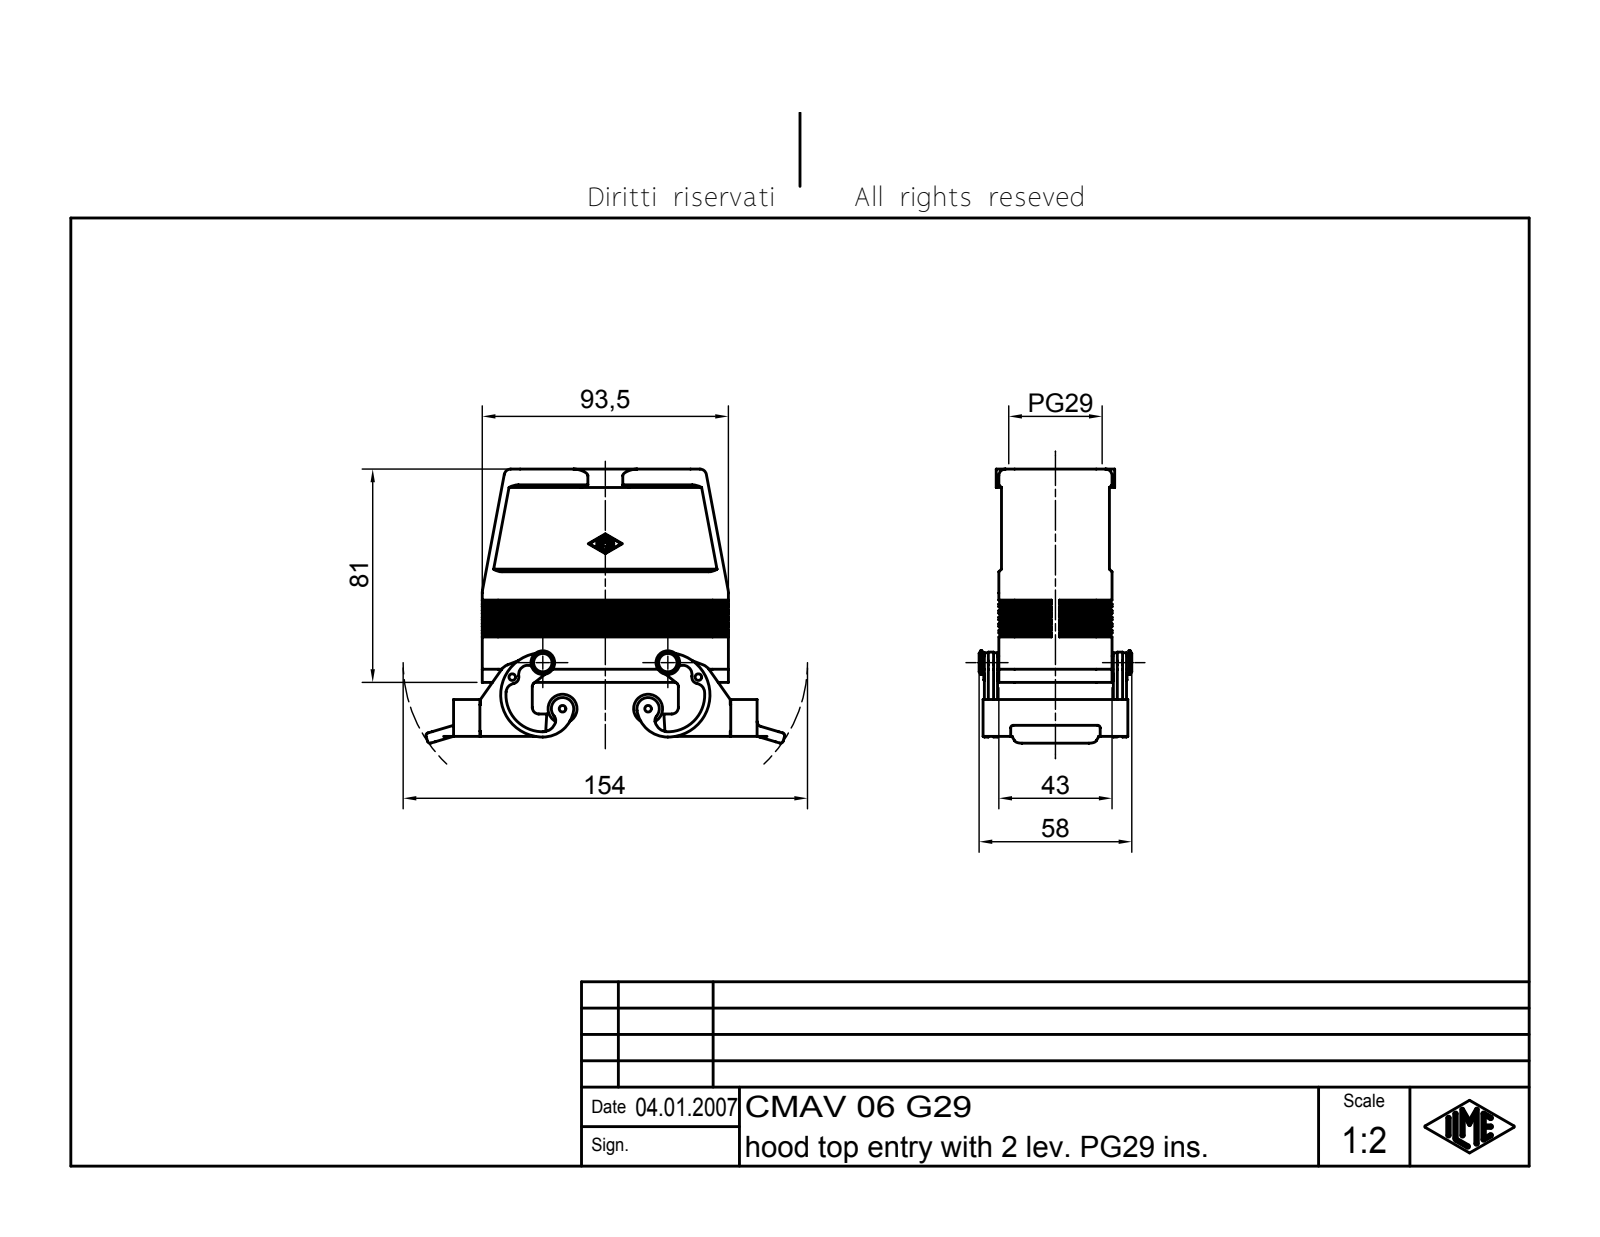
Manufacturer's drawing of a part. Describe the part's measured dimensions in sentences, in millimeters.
The part is named "CAV Tüllengehäuse 2 Bügel für einen Einsatz". Its 3-D file was written by "Autodesk Inventor 7 (AUTOMOTIVE_DESIGN)". It is 1 solid with 957 faces: 304 planar, 252 cylindrical and 401 other. Overall it measures 136.29 by 104.08 by 58 millimeters. Its volume is 107 372 cubic millimeters and its surface area 61 181 square millimeters. Round holes: 2 of diameter 2.5, 1 of diameter 35.48. Round bosses or shafts: 2 of diameter 11, 2 of diameter 9, 2 of diameter 5, 2 of diameter 2, 1 of diameter 45. Partial cylindrical surfaces (rounded edges, fillets, slot ends): 14 of radius 0.25, 12 of radius 1, 10 of radius 2.5, 10 of radius 6, 8 of radius 3, 7 of radius 2, 4 of radius 3.5, 4 of radius 5. The main face-to-face distances are 4, 3, 39, 38, 35, 1, 42, 43, 41, 2. The hole center spacings are 70.7.
